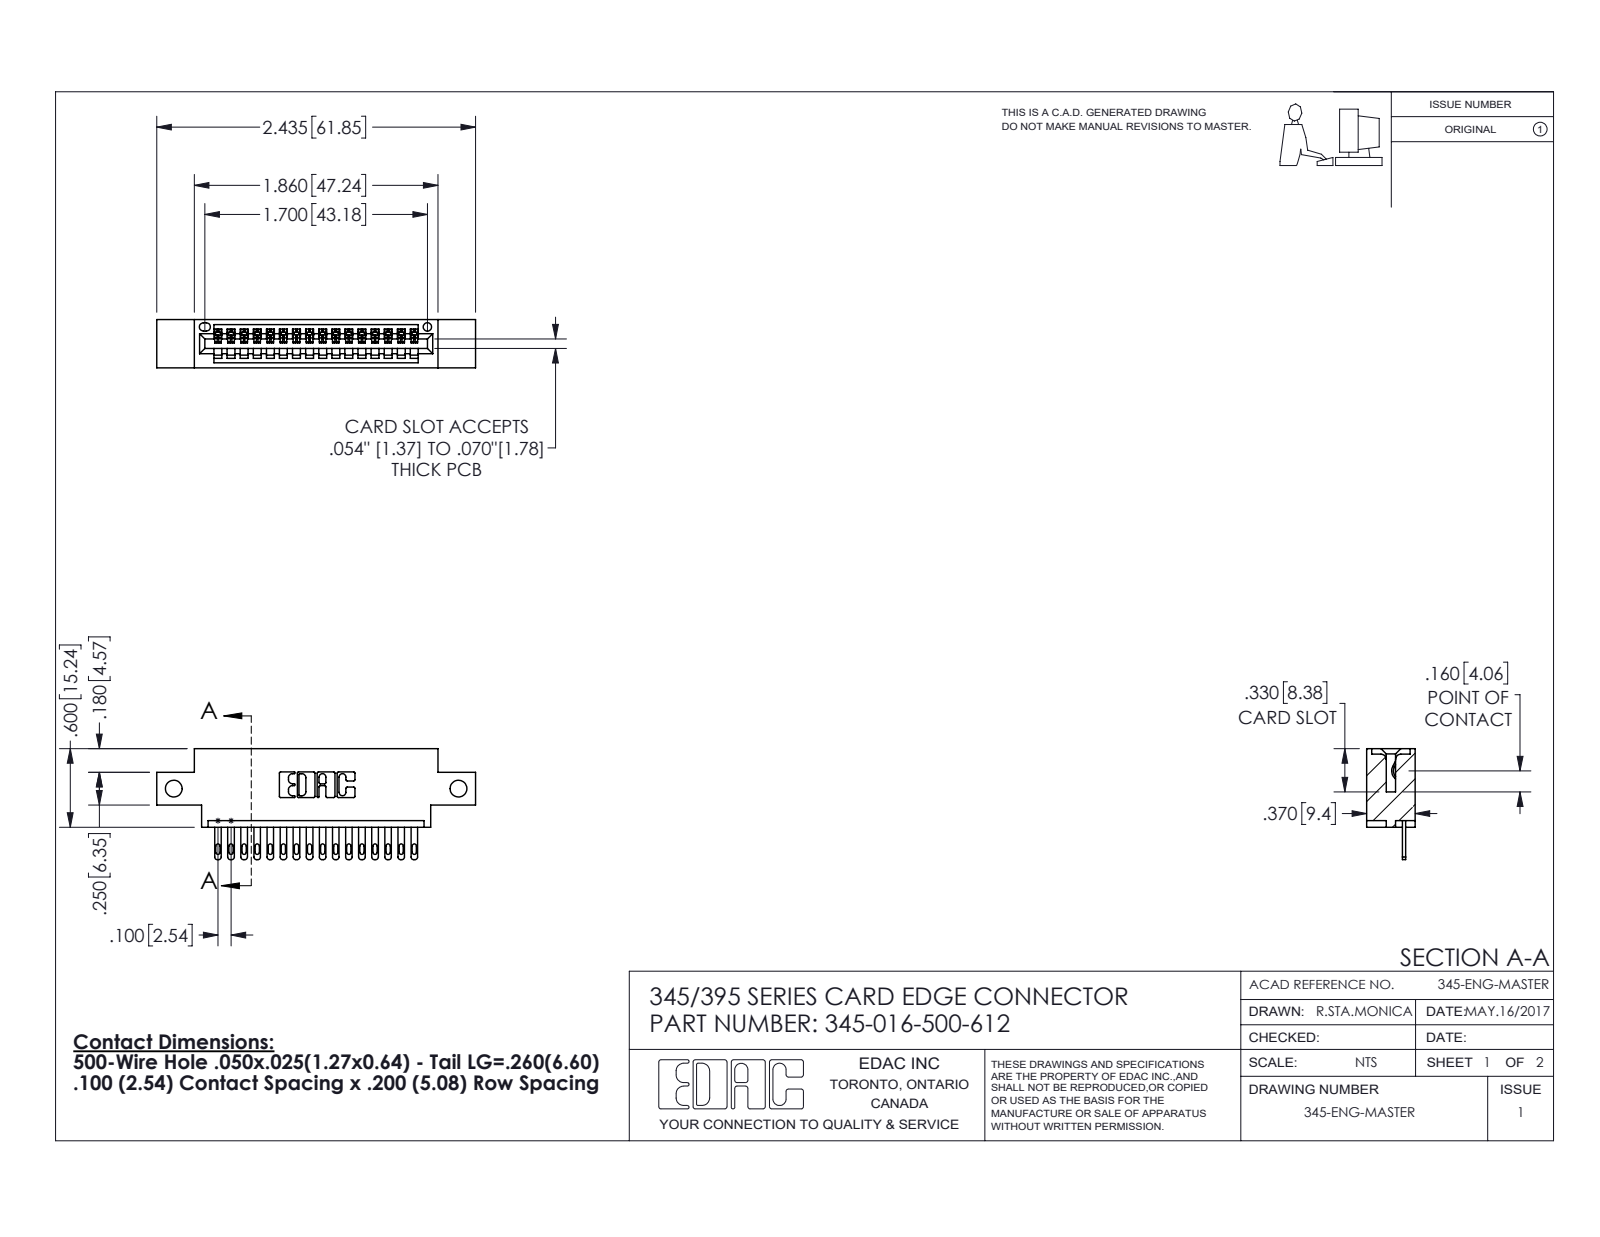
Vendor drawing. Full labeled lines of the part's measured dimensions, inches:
Part name (STEP PRODUCT): 345 Part_0.170 Offset - Side Mount; 345-292-001_345-293-100; 345-016-500-612
STEP written by: SolidWorks 2016 (CONFIG_CONTROL_DESIGN)
Units: inches
Bodies: 17 solids, 994 faces (628 planar, 366 cylindrical, 0 other)
Overall size (bounding box): 2.435 × 0.847 × 0.37
Volume: 0.334 in³ · Surface area: 10.75 in²
Round holes (diameter × count): ⌀0.128 ×2, ⌀0.064 ×1
Partial cylindrical surfaces — rounded edges, fillets, slot ends (radius × count): R0.006 ×32, R0.016 ×32, R0.02 ×32, R0.01 ×22, R0.007 ×6, R0.031 ×6, R0.026 ×3, R0.031 ×2
Main face-to-face distances: 0.298, 0.072, 0.37, 0.2, 0.098, 0.272, 0.025, 0.1, 0.225, 0.15
Hole centre spacings: 2.175
